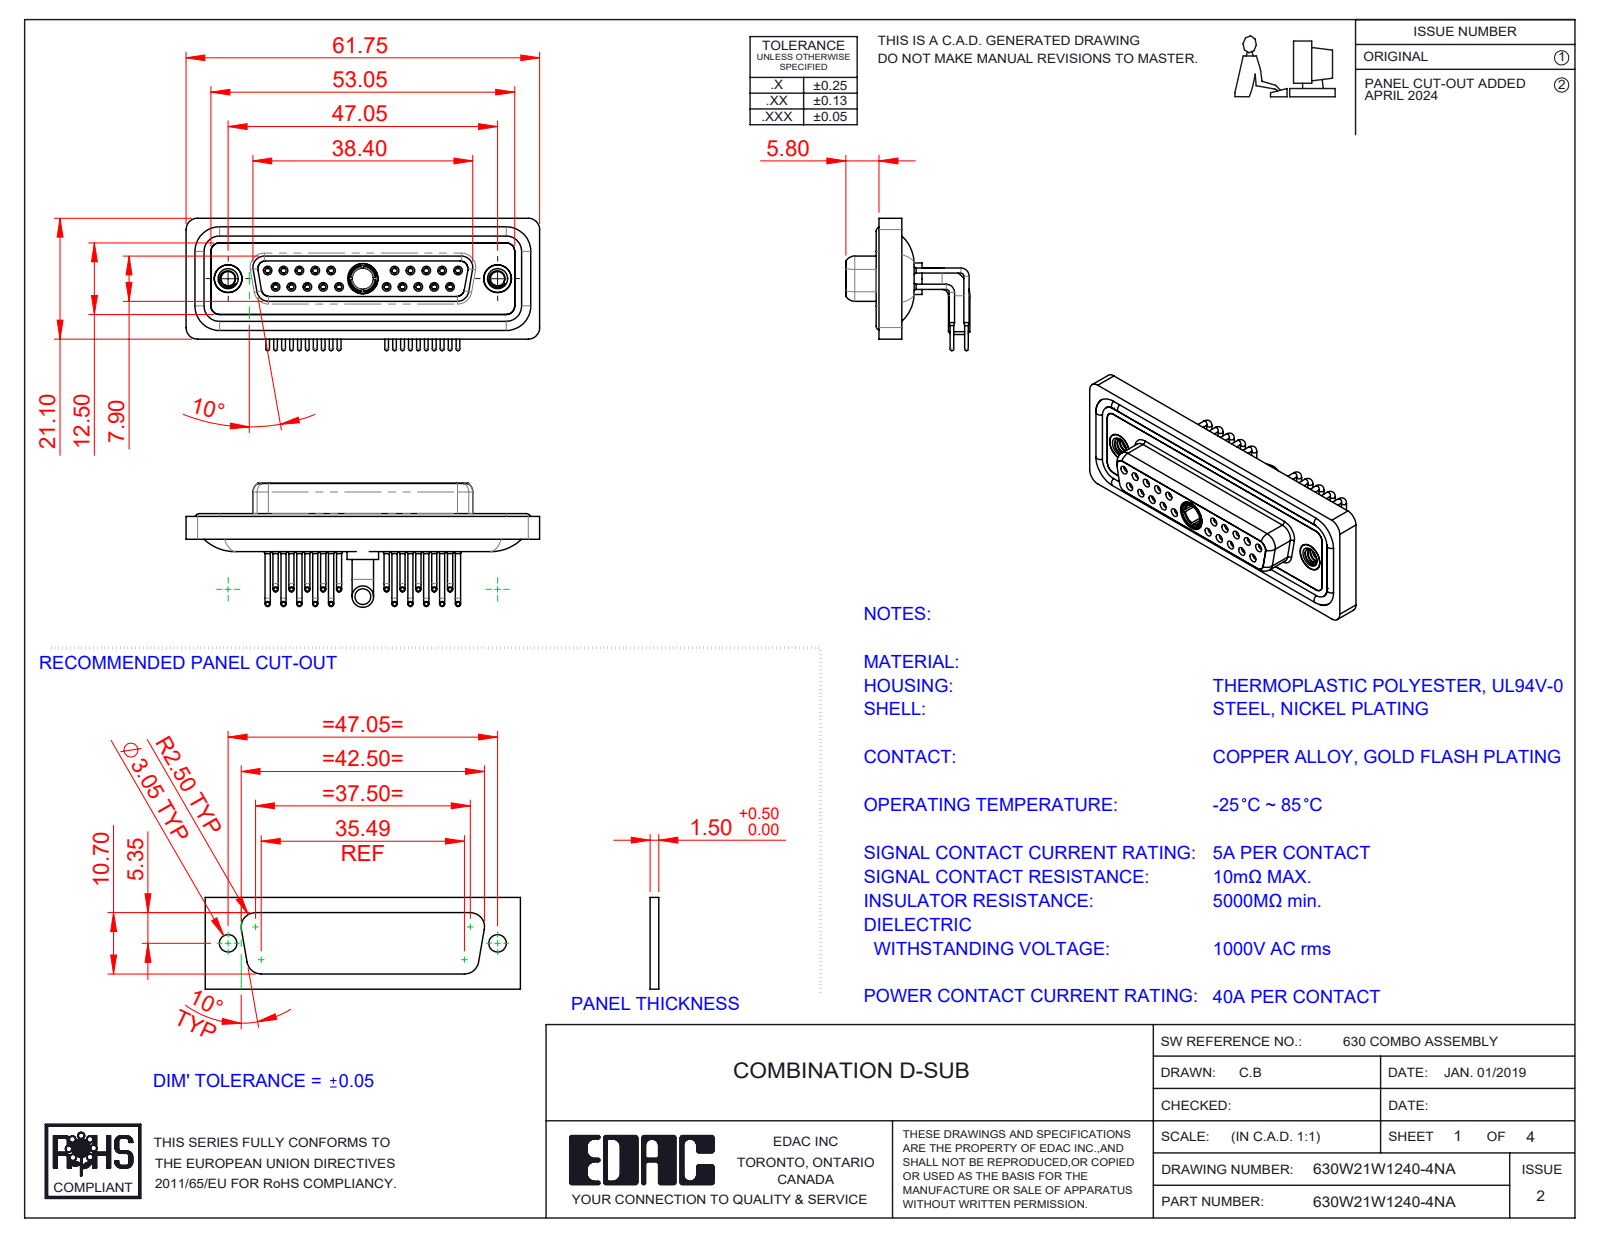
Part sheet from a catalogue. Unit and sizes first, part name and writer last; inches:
Units: inches
Overall size (bounding box): 2.431 × 0.91 × 0.854
Round holes (diameter × count): ⌀0.035 ×20, ⌀0.043 ×20, ⌀0.059 ×20, ⌀0.079 ×20, ⌀0.063 ×10, ⌀0.067 ×10, ⌀0.191 ×3, ⌀0.098 ×2, ⌀0.157 ×2, ⌀0.159 ×2, ⌀0.197 ×2, ⌀0.146 ×1
Round bosses / shafts (diameter × count): ⌀0.035 ×20, ⌀0.026 ×20, ⌀0.063 ×14, ⌀0.195 ×2, ⌀0.189 ×2, ⌀0.148 ×2, ⌀0.217 ×1, ⌀0.205 ×1
Partial cylindrical surfaces — rounded edges, fillets, slot ends (radius × count): R0.059 ×18, R0.079 ×18, R0.053 ×8, R0.063 ×8, R0.01 ×4, R0.02 ×4, R0.024 ×4, R0.026 ×4
Main face-to-face distances: 0.016, 0.071, 0.161, 0.063, 0.043, 0.098, 0.122, 0.059, 0.386, 0.018
Hole centre spacings: 0.124, 0.109, 0.218, 0.327, 0.198, 0.763, 0.826, 0.872
Volume: 0.523 in³ · Surface area: 22.98 in²
Bodies: 29 solids, 1518 faces (434 planar, 671 cylindrical, 413 other)
Part name (STEP PRODUCT): 630Combo Shell Front_25 Contacts; 630Combo Contact Row 1_50 Contacts; 630Combo Waterproof Housing_25 Contacts; Power Socket_40A RA (+5 more)
STEP written by: SolidWorks 2023 (CONFIG_CONTROL_DESIGN)
